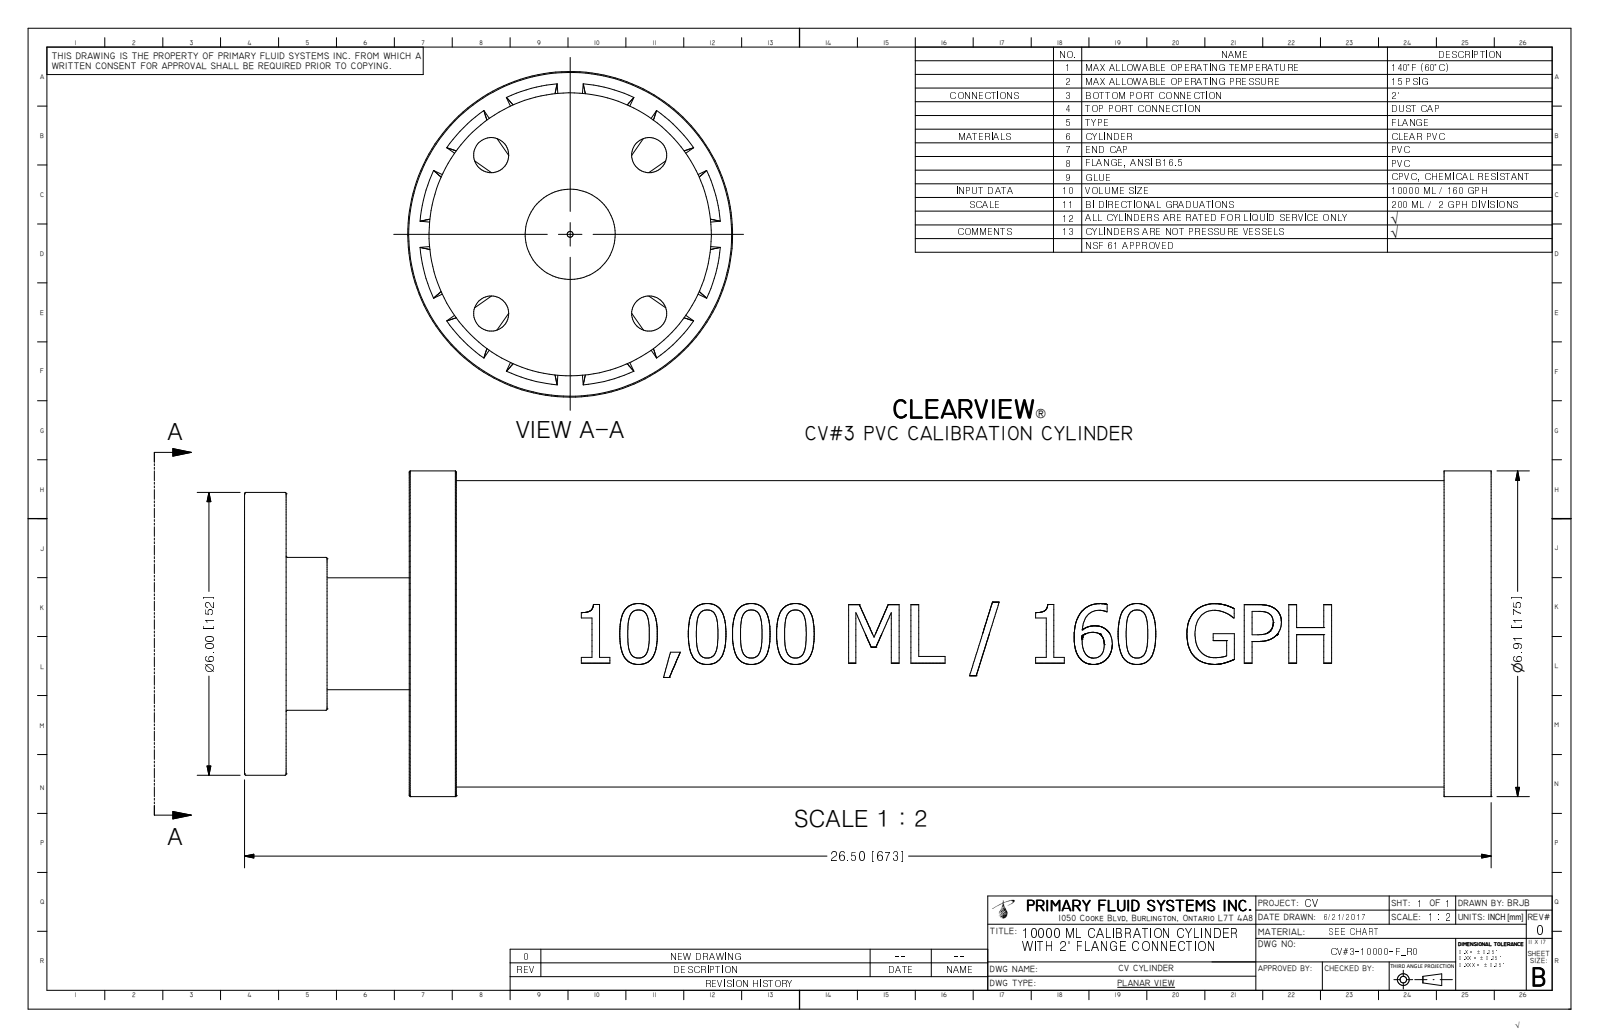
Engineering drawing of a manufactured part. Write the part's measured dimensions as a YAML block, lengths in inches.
part_name: "PV#3-10000-F_R0"
step_written_by: "Autodesk Inventor 2009 (AUTOMOTIVE_DESIGN)"
units: inches
bodies: {solids: 1, faces: 324, planar: 101, cylindrical: 36, other: 187}
overall_size: [26.5, 6.906, 6.906]
volume: 130.1
surface_area: 1256
round_holes:
  - {diameter: 0.745, count: 4}
  - {diameter: 1.913, count: 1}
  - {diameter: 1.939, count: 1}
  - {diameter: 6.32, count: 1}
round_bosses_or_shafts:
  - {diameter: 6.906, count: 1}
  - {diameter: 6.5, count: 1}
  - {diameter: 6, count: 1}
  - {diameter: 3.244, count: 1}
  - {diameter: 2.375, count: 1}
partial_cylinders:
  - {radius: 3.249, count: 1}
face_to_face_distances: [1, 25.5, 26.5, 0.885, 24.615, 25.615, 4, 3.115, 21.5, 22.5]
hole_center_spacings: [2.375, 3.359, 4.75]
